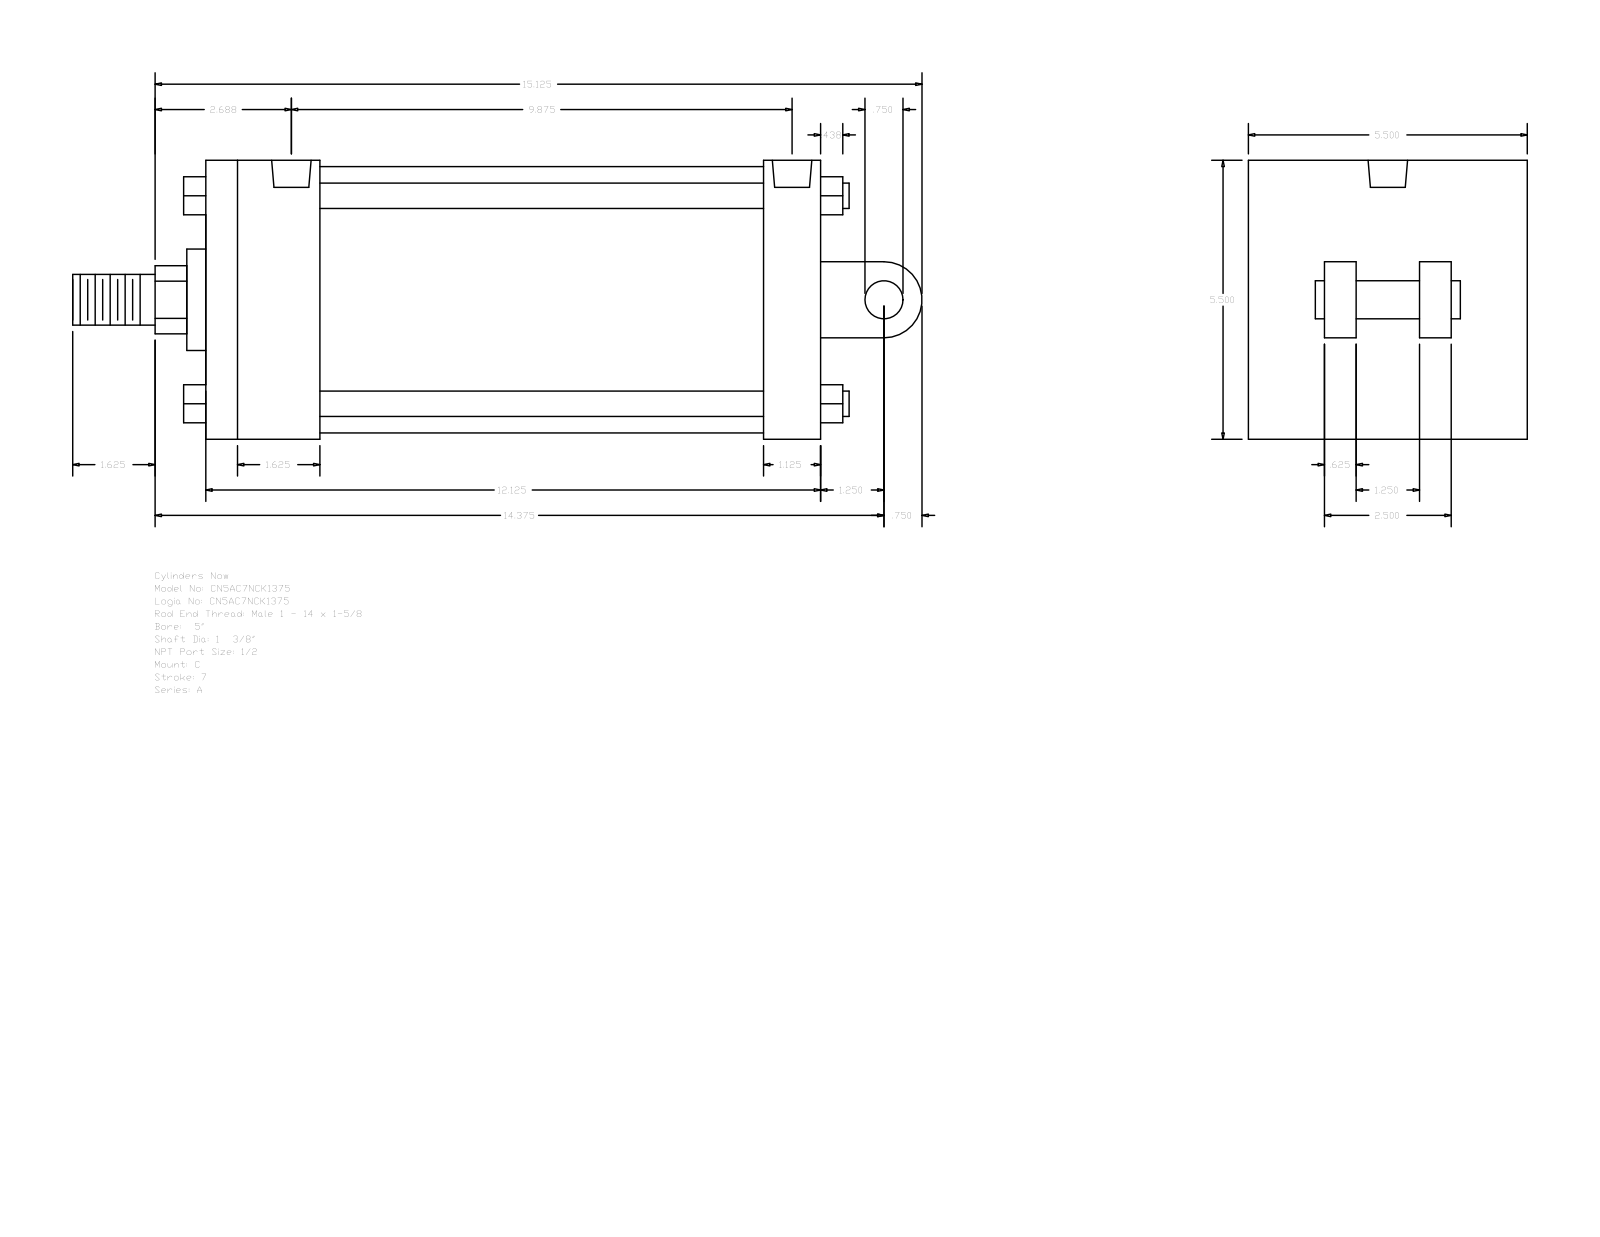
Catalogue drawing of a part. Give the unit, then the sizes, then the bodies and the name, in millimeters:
Units: millimetres
Overall size (bounding box): 425.45 × 139.7 × 139.7
Round holes (diameter × count): ⌀8.73 ×4, ⌀19.77 ×2
Round bosses / shafts (diameter × count): ⌀12.7 ×4, ⌀133.35 ×1, ⌀50.8 ×1, ⌀34.92 ×1, ⌀25.4 ×1, ⌀19.05 ×1
Partial cylindrical surfaces — rounded edges, fillets, slot ends (radius × count): R17.06 ×1, R19.05 ×1
Main face-to-face distances: 139.7, 307.98, 57.15, 28.58, 279.4, 222.25, 250.83, 38.1, 53.97, 101.6
Hole centre spacings: 2.39, 246.05, 248.44, 250.83
Bodies: 0 solids, 135 faces (102 planar, 33 cylindrical, 0 other)
Part name (STEP PRODUCT): A_C__0500_1.375
STEP written by: GSSL Pune (CONFIG_CONTROL_DESIGN)
